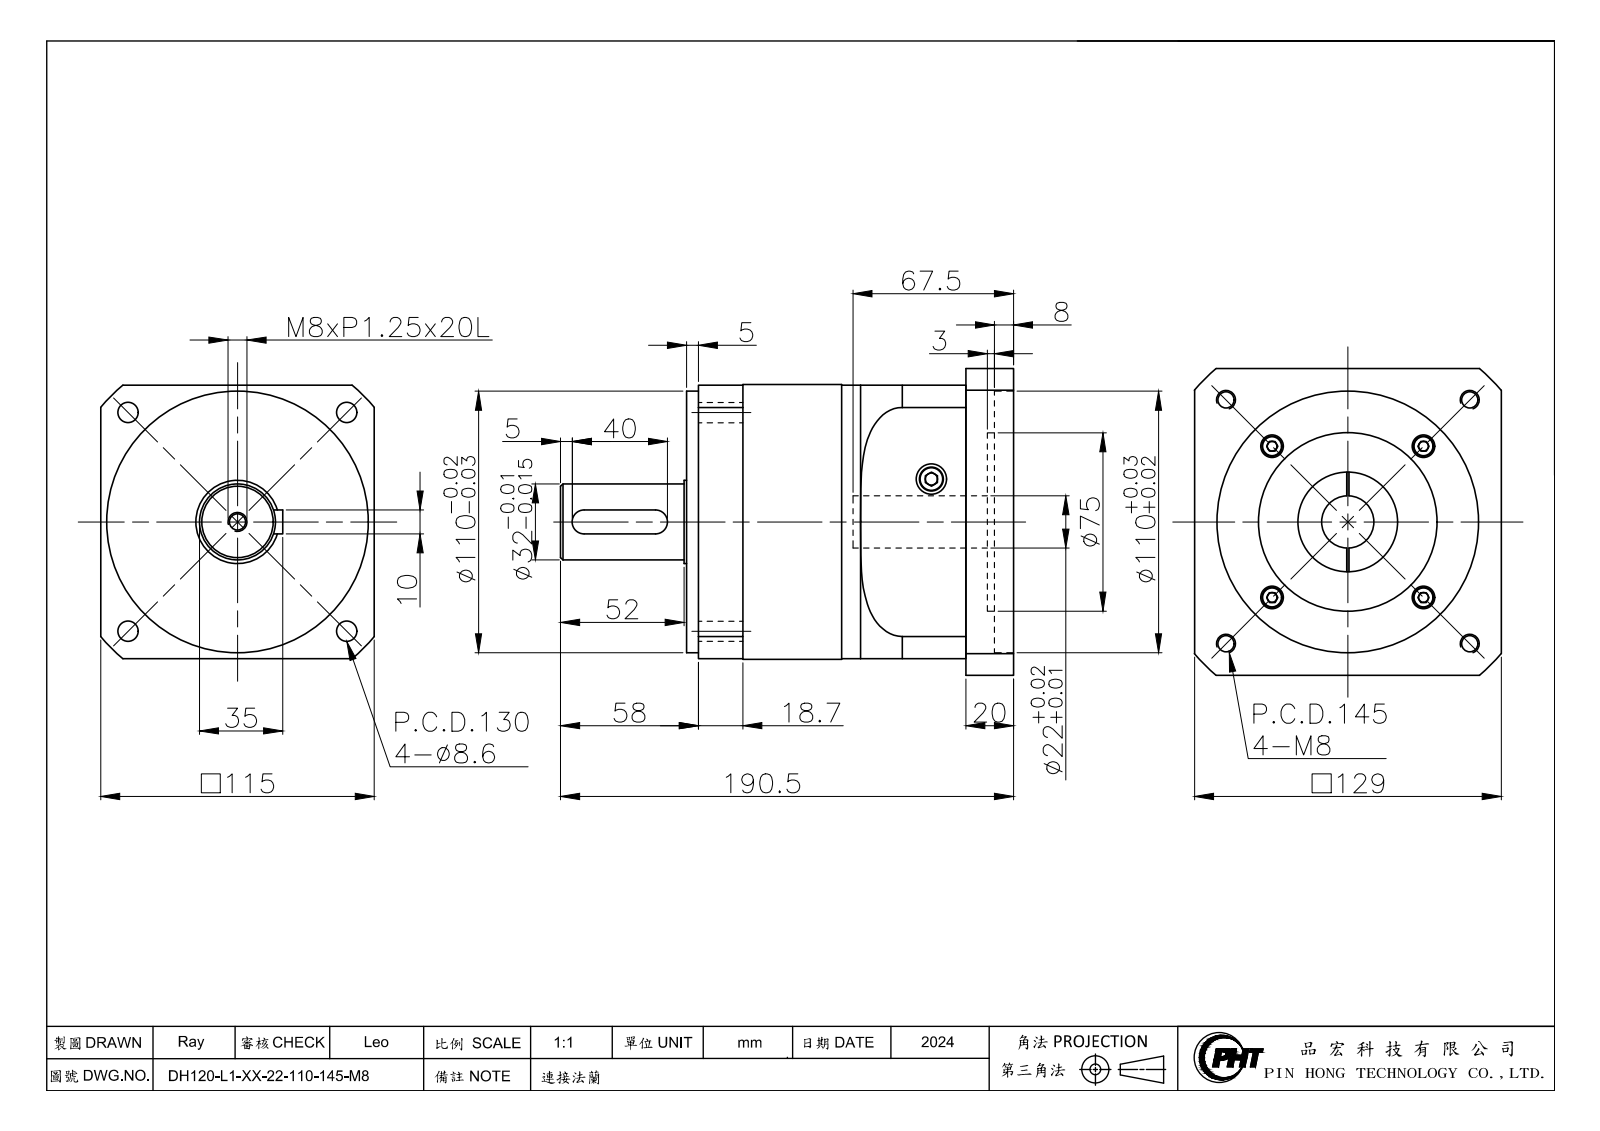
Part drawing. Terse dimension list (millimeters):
name: DH120-L1-XX-22-110-145-M8(連接法蘭)_2024
written by: SolidWorks 2016 (CONFIG_CONTROL_DESIGN)
unit: mm
bodies: 2 solids, 343 faces (158 planar, 137 cylindrical, 48 other)
size: 190.5 × 129 × 129
volume: 1 552 000 mm³; area: 167 905 mm²
holes: 8× ⌀9.5, 5× ⌀6.8, 4× ⌀4.2, 4× ⌀5.5, 4× ⌀8.6, 4× ⌀10, 2× ⌀12.7, 1× ⌀22, 1× ⌀42, 1× ⌀60, 1× ⌀70, 1× ⌀75
bosses: 12× ⌀8.5, 4× ⌀5, 1× ⌀115.5, 1× ⌀115, 1× ⌀49, 1× ⌀35, 1× ⌀32
rounds: 2× R5, 1× R75, 1× R85
face distances: 115, 7, 122, 117.5, 20, 137.5, 8, 12, 129.5, 5
hole spacings: 54, 15.71, 18.98, 24.68, 60.69, 72.96, 76.37, 78.4
